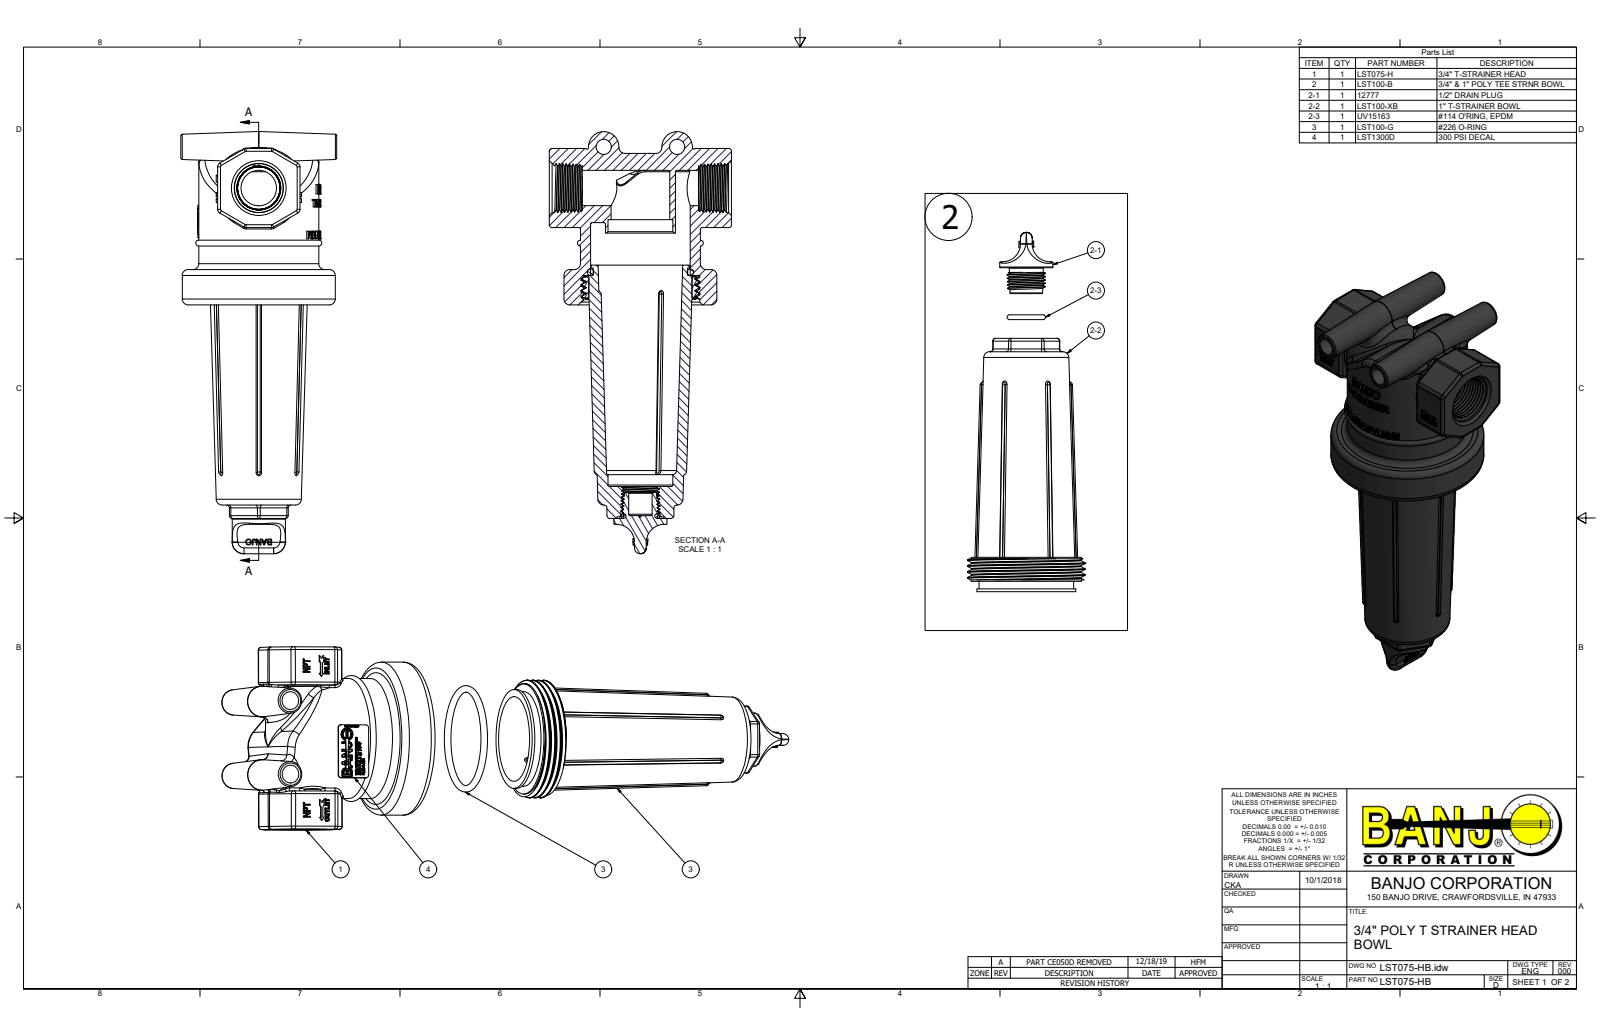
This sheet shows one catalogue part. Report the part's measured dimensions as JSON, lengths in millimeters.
{"part_name": "LST075-HB; CE050D; LST075-H; LST100-B (+5 more)", "step_written_by": "Autodesk Inventor 2018 (AUTOMOTIVE_DESIGN)", "units": "millimeters", "bodies": {"solids": 8, "faces": 2521, "planar": 1368, "cylindrical": 229, "other": 924}, "overall_size": [361.9, 98.3, 84.2], "volume_mm3": 304600, "surface_area_mm2": 165200, "round_holes": [[4.6, 1], [6.5, 1], [12.7, 1], [19.1, 1], [25.5, 1], [31.8, 1], [35.1, 1], [53.8, 1], [55.8, 1], [60.9, 1], [64.1, 1]], "round_bosses_or_shafts": [[82.6, 1], [64.8, 1], [63.5, 1], [59.4, 1], [53.3, 1], [51.1, 1], [37.8, 1], [37.3, 1]], "partial_cylinders_radius": [[1.5, 52], [0.8, 11], [2.4, 8], [0.7, 2], [0.8, 2], [0.9, 2], [1.6, 2], [1.8, 2]], "face_to_face_distances": [44.5, 15.9, 17.8, 15.1, 0.8, 3.7, 12.2, 11.4, 6.4, 98.3]}
